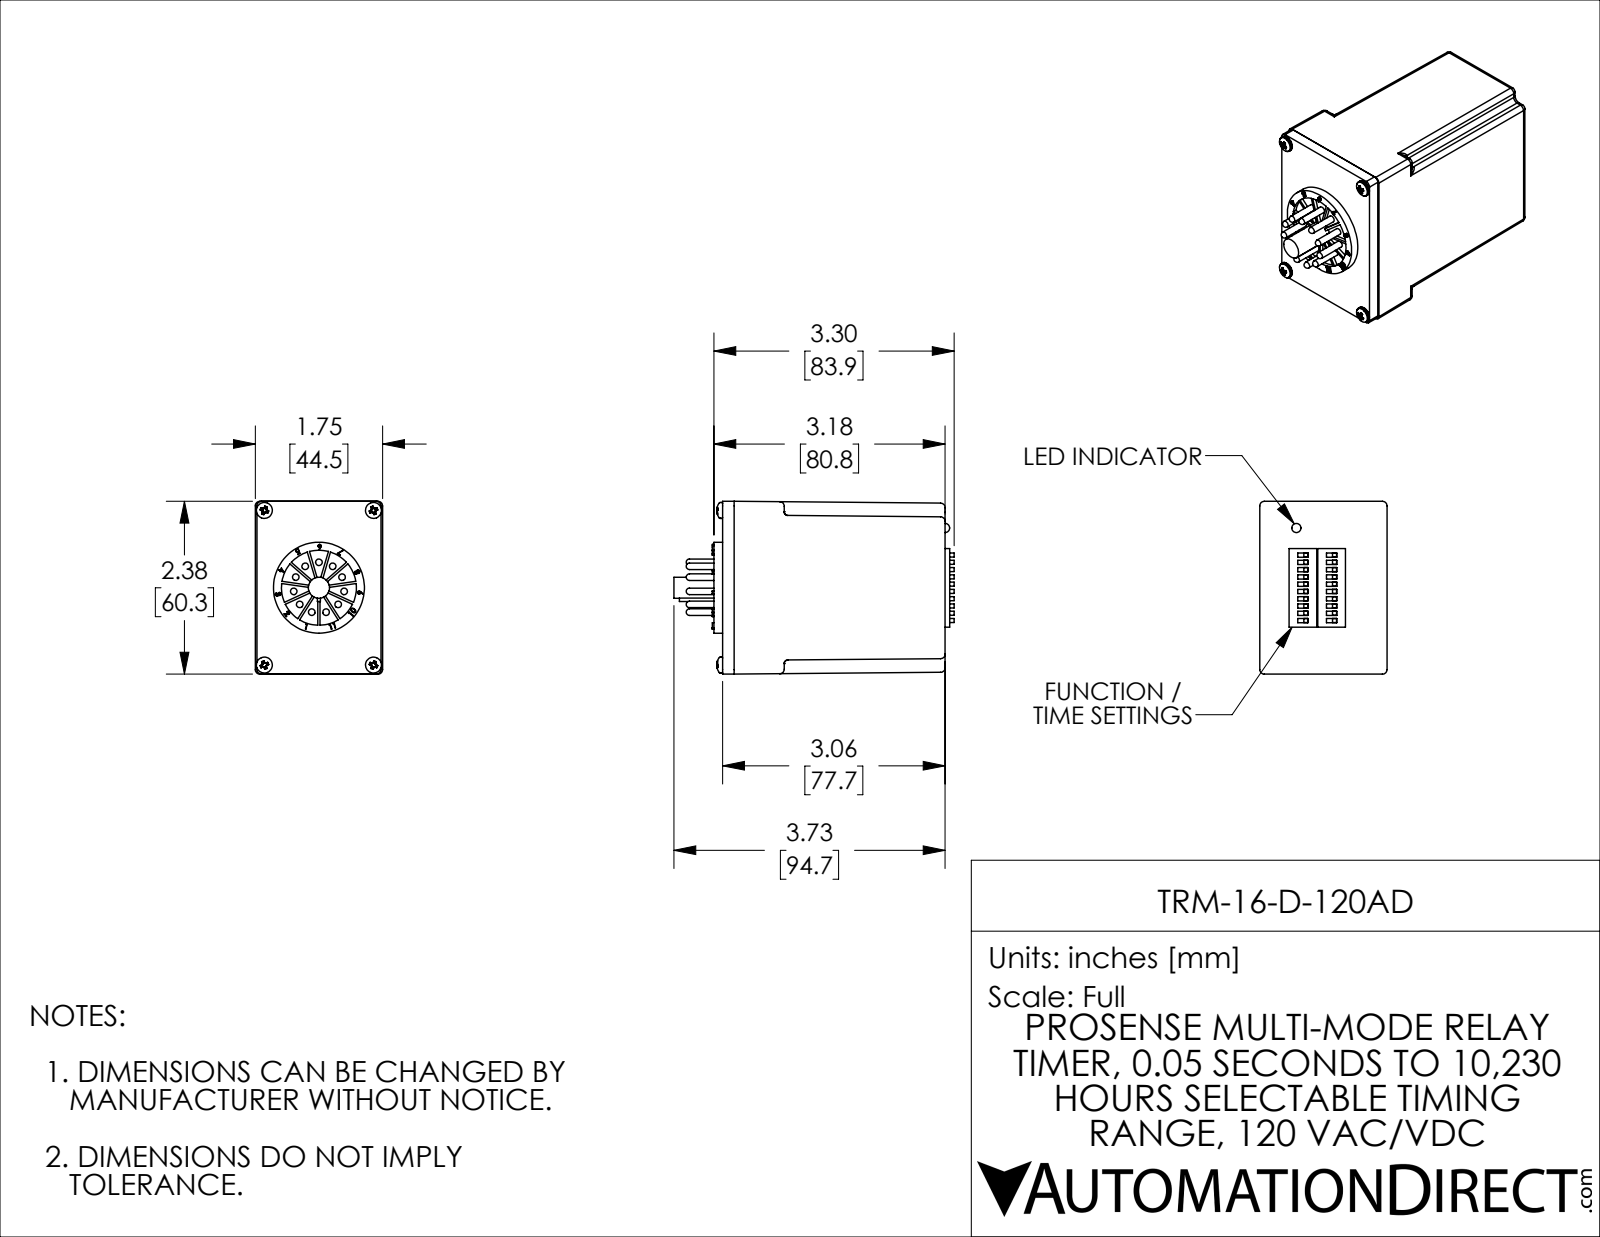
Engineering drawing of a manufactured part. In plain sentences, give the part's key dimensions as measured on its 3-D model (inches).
The part is named "TRM-16-D-120AD". Its 3-D file was written by "SolidWorks 2021 (CONFIG_CONTROL_DESIGN)". It is 41 solids with 800 faces: 463 planar, 158 cylindrical and 179 other. Overall it measures 3.853 by 2.375 by 1.75 inches. Its volume is 12.3 cubic inches and its surface area 49.29 square inches. Round holes: 4 of diameter 0.125, 1 of diameter 1.03. Round bosses or shafts: 11 of diameter 0.09, 4 of diameter 0.219, 1 of diameter 1.25, 1 of diameter 0.29. Partial cylindrical surfaces (rounded edges, fillets, slot ends): 32 of radius 0.063, 4 of radius 0.05. The main face-to-face distances are 0.16, 3.06, 2.9, 3.193, 0.05, 0.07, 0.23, 3.13, 0.063, 3.123. The hole center spacings are 1.301, 1.5, 2.125, 2.601.
